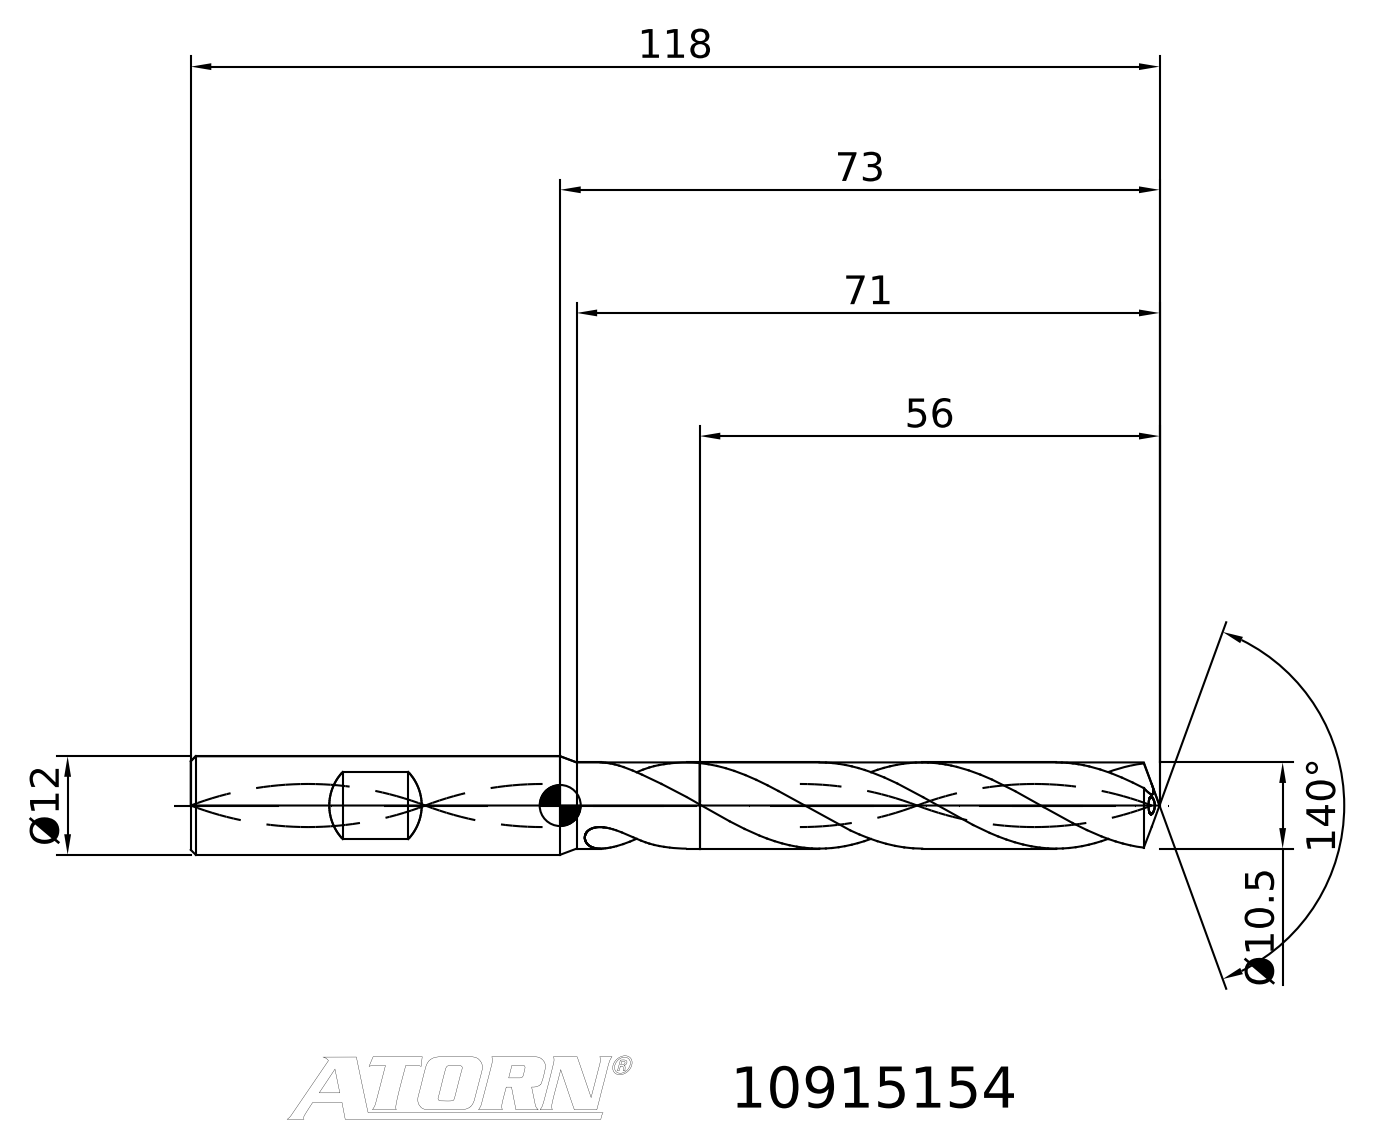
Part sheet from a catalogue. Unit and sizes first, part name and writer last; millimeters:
Units: millimetres
Overall size (bounding box): 118 × 27.11 × 16.44
Main face-to-face distances: 62, 54.57, 116.57
Volume: 9 288 mm³ · Surface area: 4 546 mm²
Bodies: 2 solids, 34 faces (8 planar, 0 cylindrical, 26 other)
STEP written by: TDM (AUTOMOTIVE_DESIGN)
